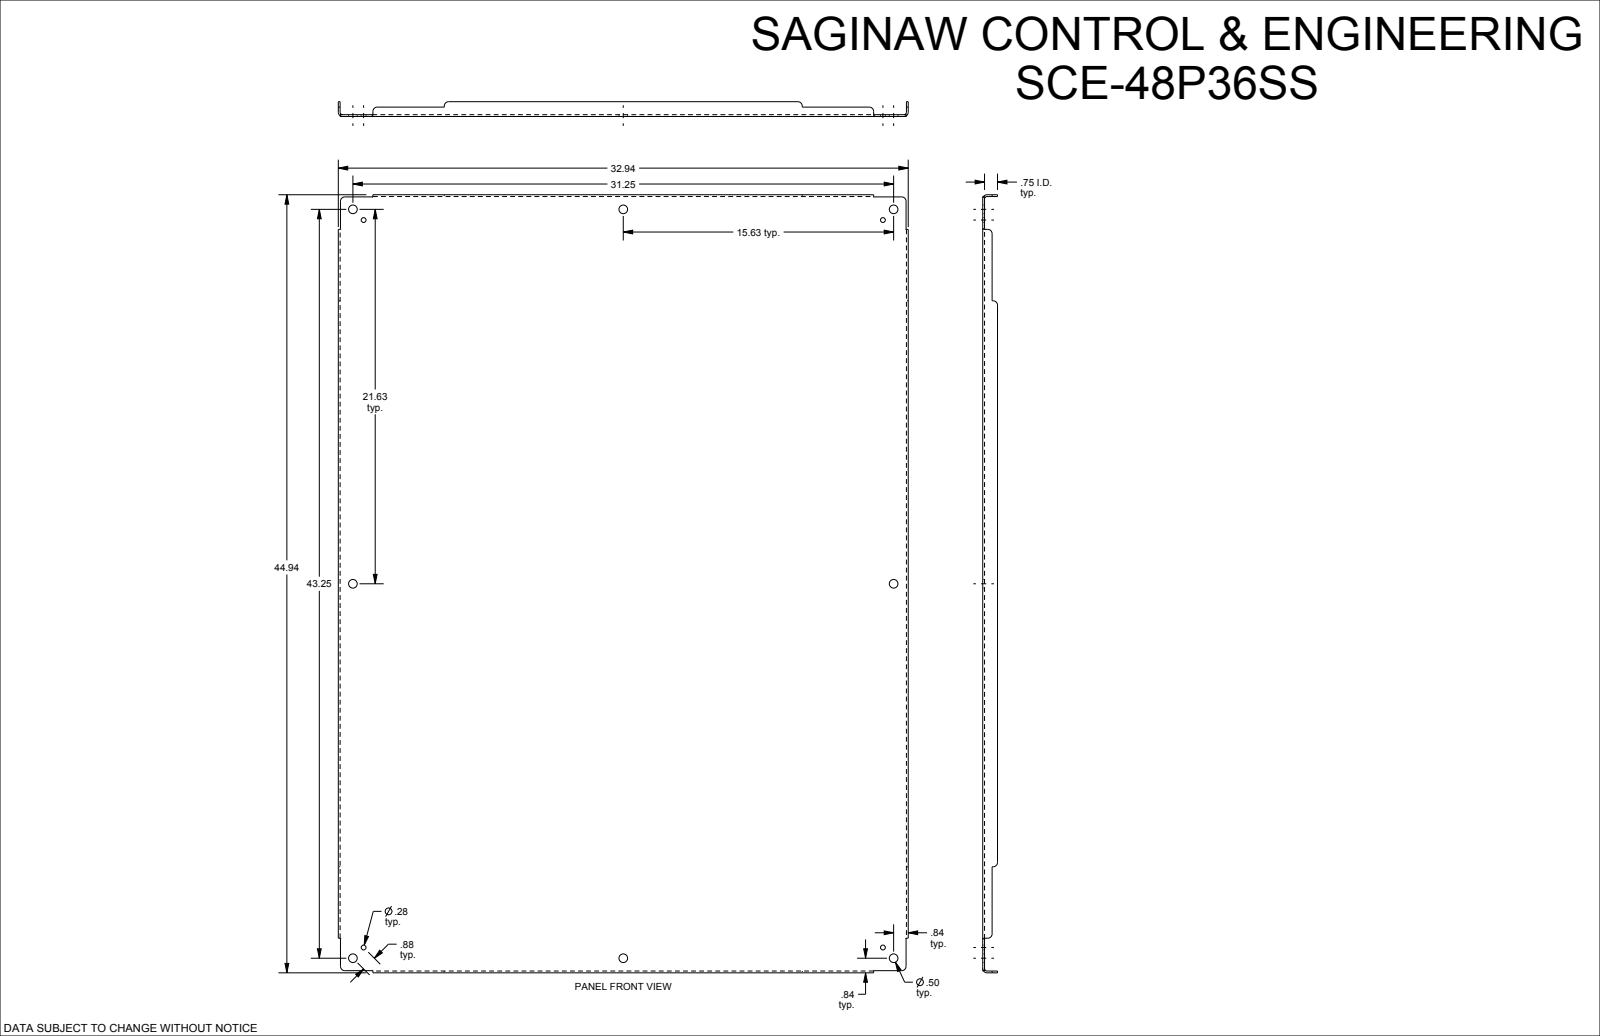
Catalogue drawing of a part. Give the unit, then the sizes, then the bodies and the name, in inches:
Units: inches
Overall size (bounding box): 44.938 × 32.938 × 0.854
Round holes (diameter × count): ⌀0.5 ×8, ⌀0.281 ×4
Partial cylindrical surfaces — rounded edges, fillets, slot ends (radius × count): R0.25 ×12, R0.246 ×4, R0.142 ×2, R0.143 ×2
Main face-to-face distances: 0.104, 0.104, 32.833, 44.833, 32.729, 32.938, 44.938, 44.729, 0.75, 0.854
Hole centre spacings: 0.875, 15.019, 15.625, 21.015, 21.625, 26.679, 30.638, 37.143
Volume: 162.1 in³ · Surface area: 3 136 in²
Bodies: 1 solid, 110 faces (46 planar, 40 cylindrical, 24 other)
Part name (STEP PRODUCT): SCE-48P36SS
STEP written by: SolidWorks 2019 (CONFIG_CONTROL_DESIGN)
